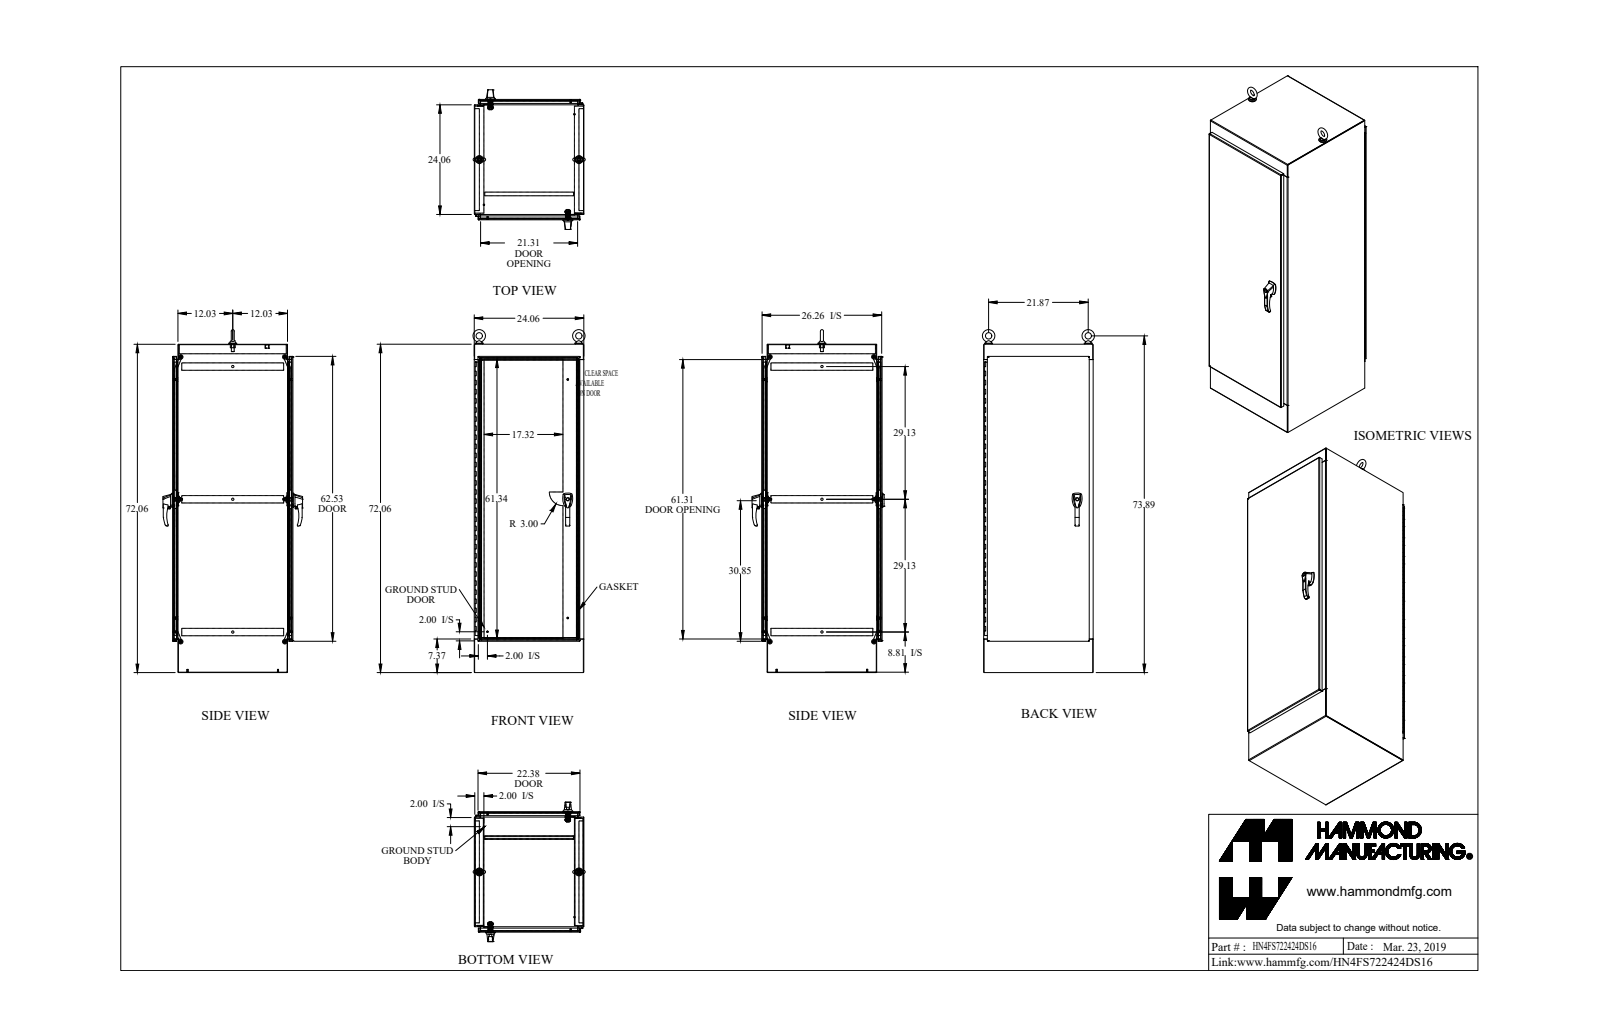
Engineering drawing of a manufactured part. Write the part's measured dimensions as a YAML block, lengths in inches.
part_name: "HN4FS722424DS16"
step_written_by: "SolidWorks 2018 (AUTOMOTIVE_DESIGN)"
units: inches
bodies: {solids: 88, faces: 3200, planar: 1433, cylindrical: 1499, other: 268}
overall_size: [75.256, 30.664, 24.604]
volume: 1035
surface_area: 21777
round_holes:
  - {diameter: 0.304, count: 20}
  - {diameter: 0.35, count: 8}
  - {diameter: 0.25, count: 4}
  - {diameter: 0.257, count: 4}
  - {diameter: 0.28, count: 4}
  - {diameter: 0.281, count: 4}
  - {diameter: 0.313, count: 4}
  - {diameter: 0.39, count: 4}
  - {diameter: 0.413, count: 4}
  - {diameter: 0.5, count: 3}
  - {diameter: 0.11, count: 2}
  - {diameter: 0.173, count: 2}
round_bosses_or_shafts:
  - {diameter: 1, count: 4}
  - {diameter: 0.75, count: 4}
  - {diameter: 0.63, count: 4}
  - {diameter: 0.44, count: 4}
  - {diameter: 0.37, count: 4}
  - {diameter: 0.313, count: 4}
  - {diameter: 0.281, count: 4}
  - {diameter: 0.25, count: 4}
partial_cylinders:
  - {radius: 0.125, count: 44}
  - {radius: 0.043, count: 42}
  - {radius: 0.138, count: 36}
  - {radius: 0.017, count: 32}
  - {radius: 0.048, count: 26}
  - {radius: 0.143, count: 26}
  - {radius: 0.5, count: 26}
  - {radius: 0.06, count: 21}
face_to_face_distances: [0.095, 23.965, 26.339, 23.87, 24.06, 1.187, 25.152, 26.244, 26.434, 71.965]
hole_center_spacings: [6, 23.099, 12, 25.329, 18, 28.663, 24, 32.765]
